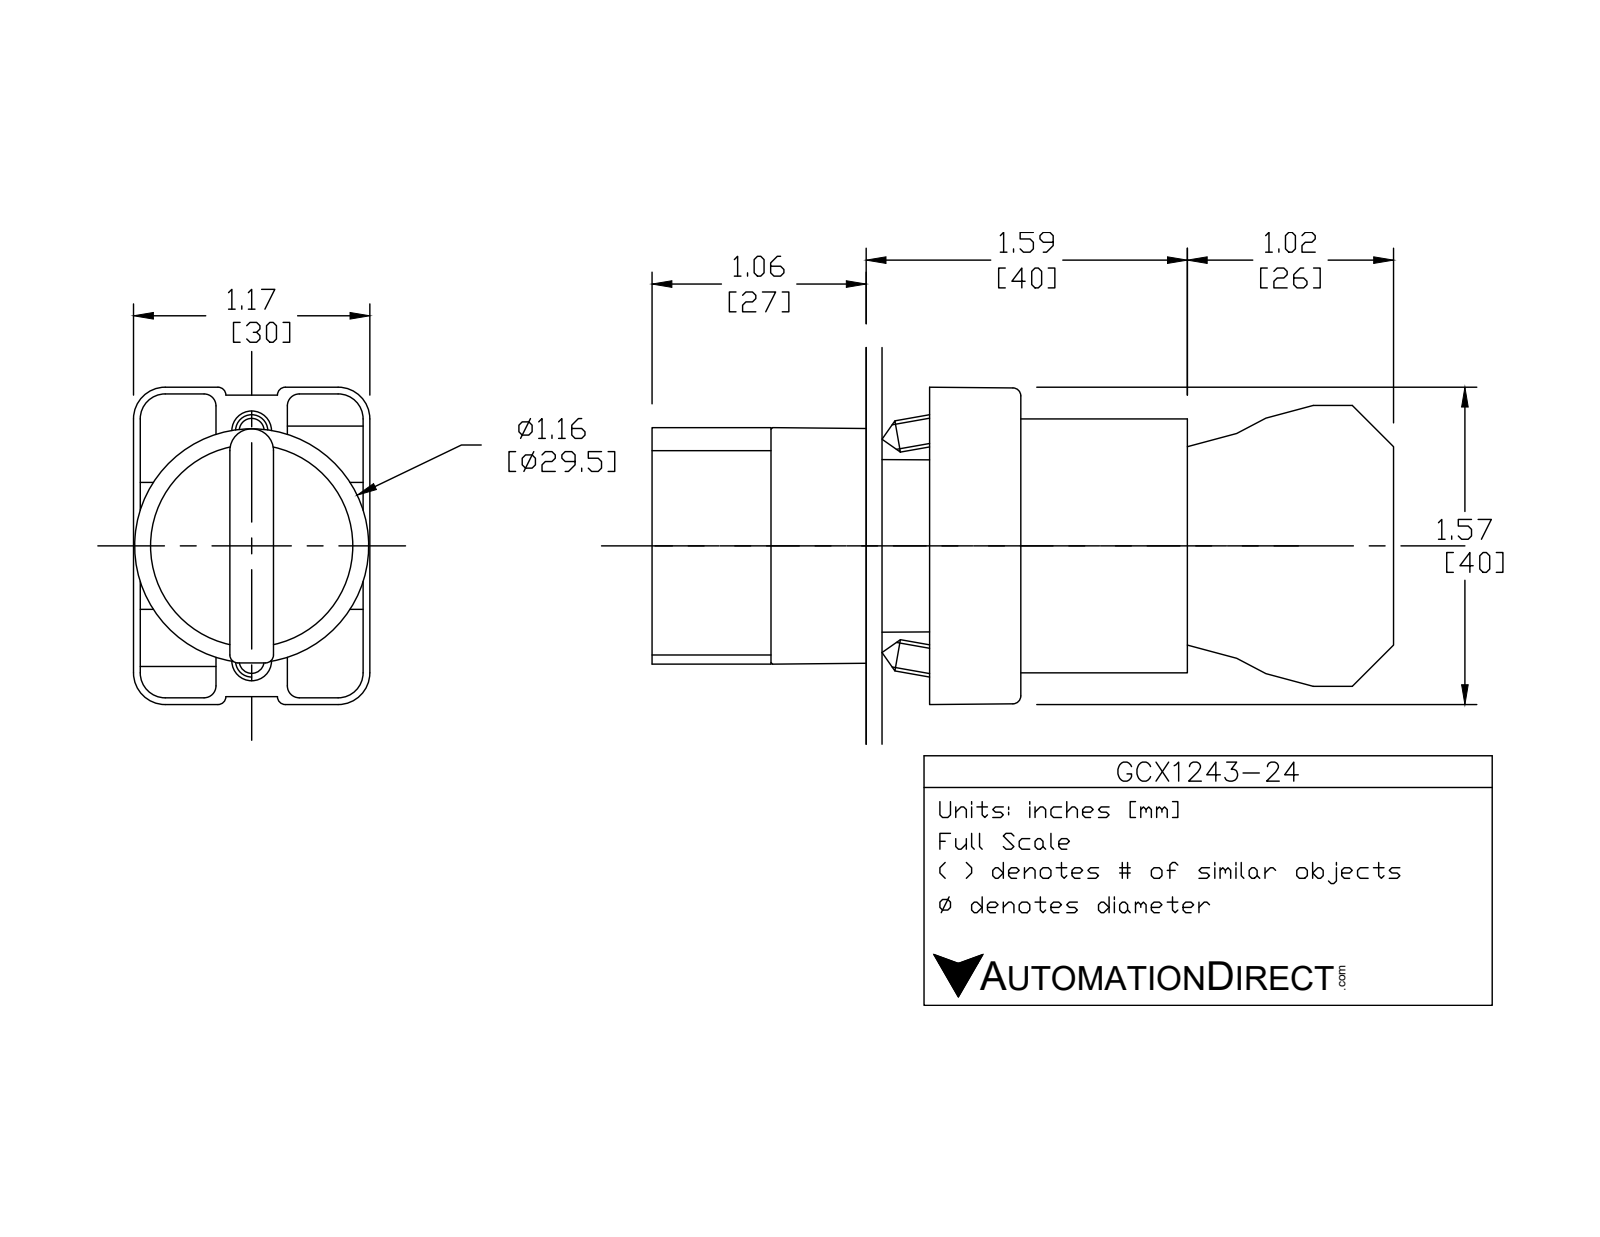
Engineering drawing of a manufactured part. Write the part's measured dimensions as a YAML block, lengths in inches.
part_name: "ecx1040; ECX1050; GCX1243 OPERATOR; ecx1029 (+1 more)"
step_written_by: "SolidWorks 2016 (AUTOMOTIVE_DESIGN)"
units: inches
bodies: {solids: 8, faces: 445, planar: 263, cylindrical: 151, other: 31}
overall_size: [3.653, 1.581, 1.177]
volume: 2.799
surface_area: 39
round_holes:
  - {diameter: 0.079, count: 2}
  - {diameter: 0.124, count: 2}
  - {diameter: 0.13, count: 2}
  - {diameter: 0.087, count: 1}
  - {diameter: 0.197, count: 1}
  - {diameter: 0.469, count: 1}
  - {diameter: 0.878, count: 1}
  - {diameter: 0.888, count: 1}
  - {diameter: 1.024, count: 1}
round_bosses_or_shafts:
  - {diameter: 0.157, count: 4}
  - {diameter: 1.175, count: 1}
  - {diameter: 1.004, count: 1}
  - {diameter: 0.945, count: 1}
  - {diameter: 0.856, count: 1}
  - {diameter: 0.78, count: 1}
  - {diameter: 0.504, count: 1}
partial_cylinders:
  - {radius: 0.059, count: 24}
  - {radius: 0.041, count: 12}
  - {radius: 0.124, count: 12}
  - {radius: 0.157, count: 12}
  - {radius: 0.039, count: 9}
  - {radius: 0.128, count: 2}
  - {radius: 0.02, count: 1}
  - {radius: 0.063, count: 1}
face_to_face_distances: [0.827, 2.02, 1.193, 0.579, 1.244, 1.171, 0.472, 0.469, 0.031, 0.033]
hole_center_spacings: [0.236, 0.544, 0.472, 0.49]
